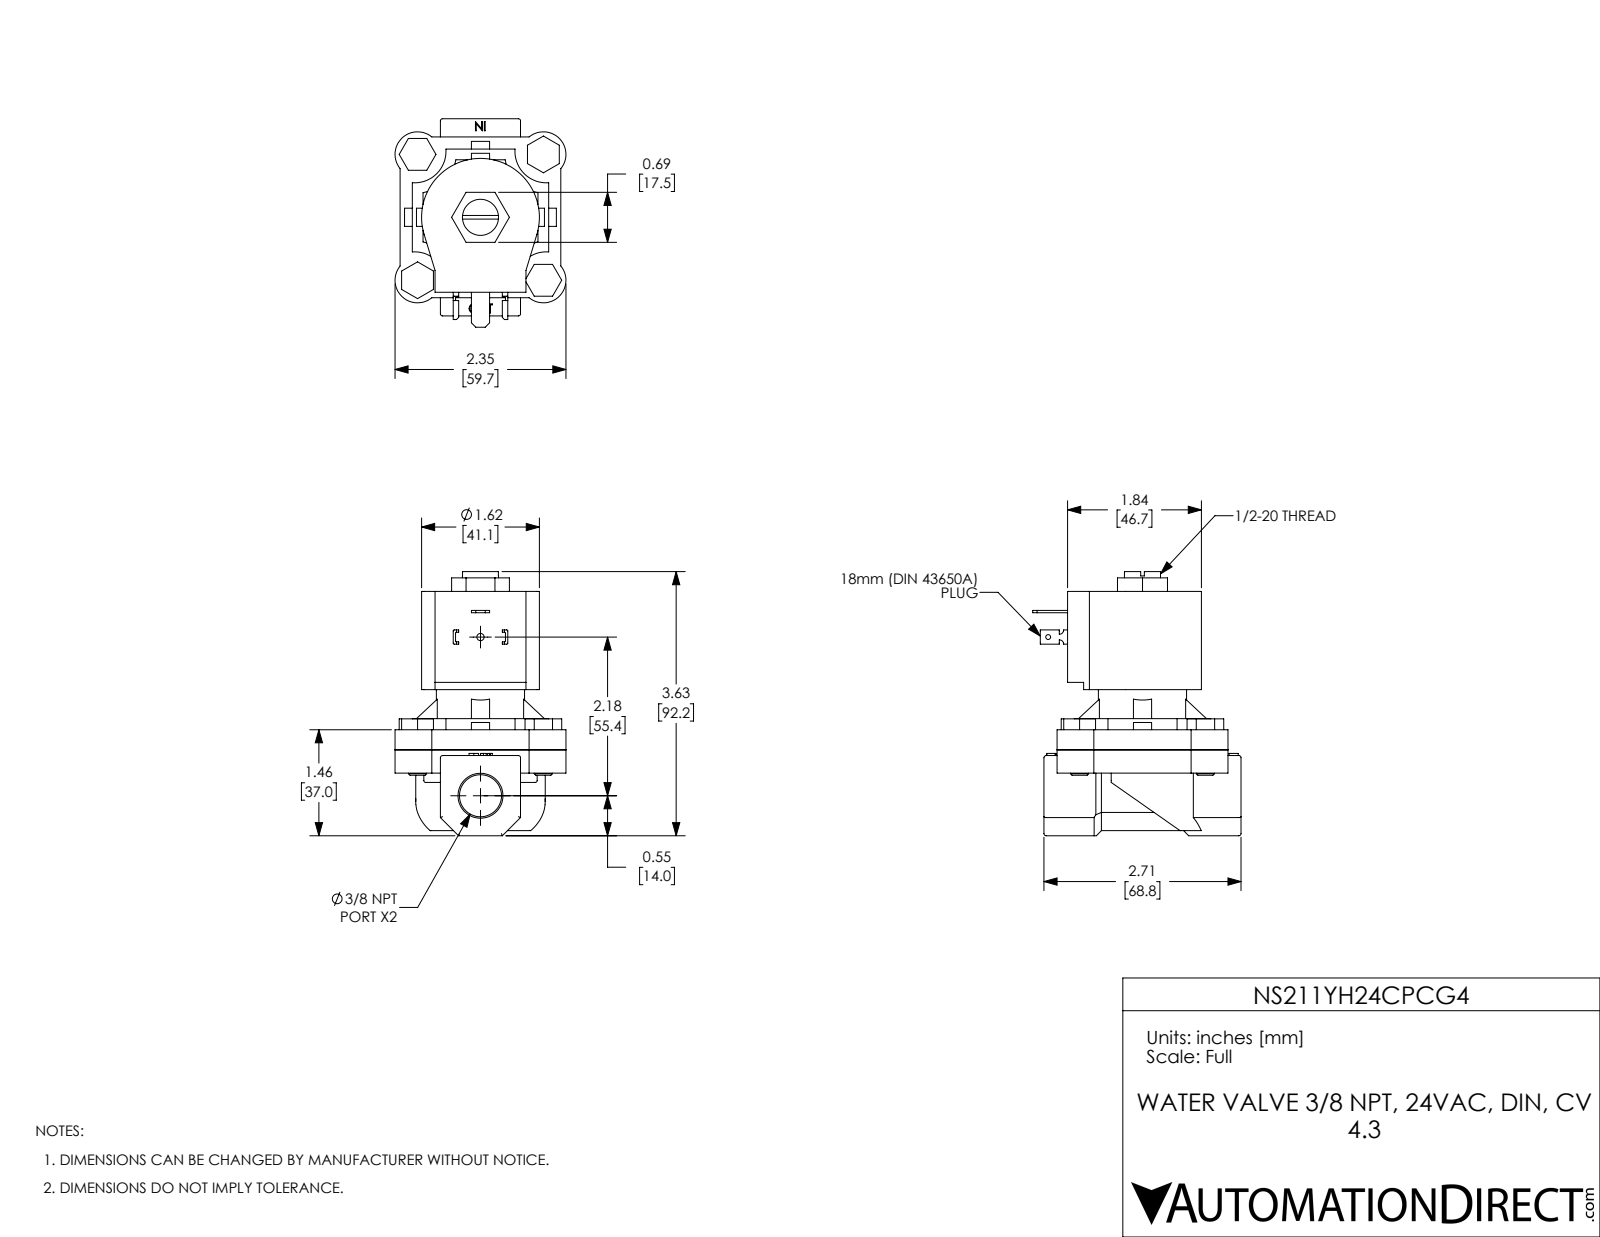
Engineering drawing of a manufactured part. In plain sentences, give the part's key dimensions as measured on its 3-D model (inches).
The part is named "NS211YH24CPCG4". Its 3-D file was written by "SolidWorks 2024 (CONFIG_CONTROL_DESIGN)". It is 11 solids with 383 faces: 237 planar, 113 cylindrical and 33 other. Overall it measures 3.63 by 2.865 by 2.35 inches. Its volume is 9.675 cubic inches and its surface area 64.2 square inches. Round holes: 4 of diameter 0.25, 1 of diameter 0.067, 1 of diameter 0.1, 1 of diameter 0.496, 1 of diameter 0.512, 1 of diameter 0.578, 1 of diameter 1.155. Round bosses or shafts: 4 of diameter 0.248, 1 of diameter 1.213. Partial cylindrical surfaces (rounded edges, fillets, slot ends): 15 of radius 0.03, 8 of radius 0.015, 4 of radius 0.31, 4 of radius 0.432, 4 of radius 0.579, 2 of radius 0.06, 1 of radius 0.81, 1 of radius 0.89. The main face-to-face distances are 0.276, 2.177, 1.901, 0.32, 0.596, 2.497, 0.554, 1.656, 0.25, 1.147. The hole center spacings are 1.223, 1.73, 2.446, 2.181.
